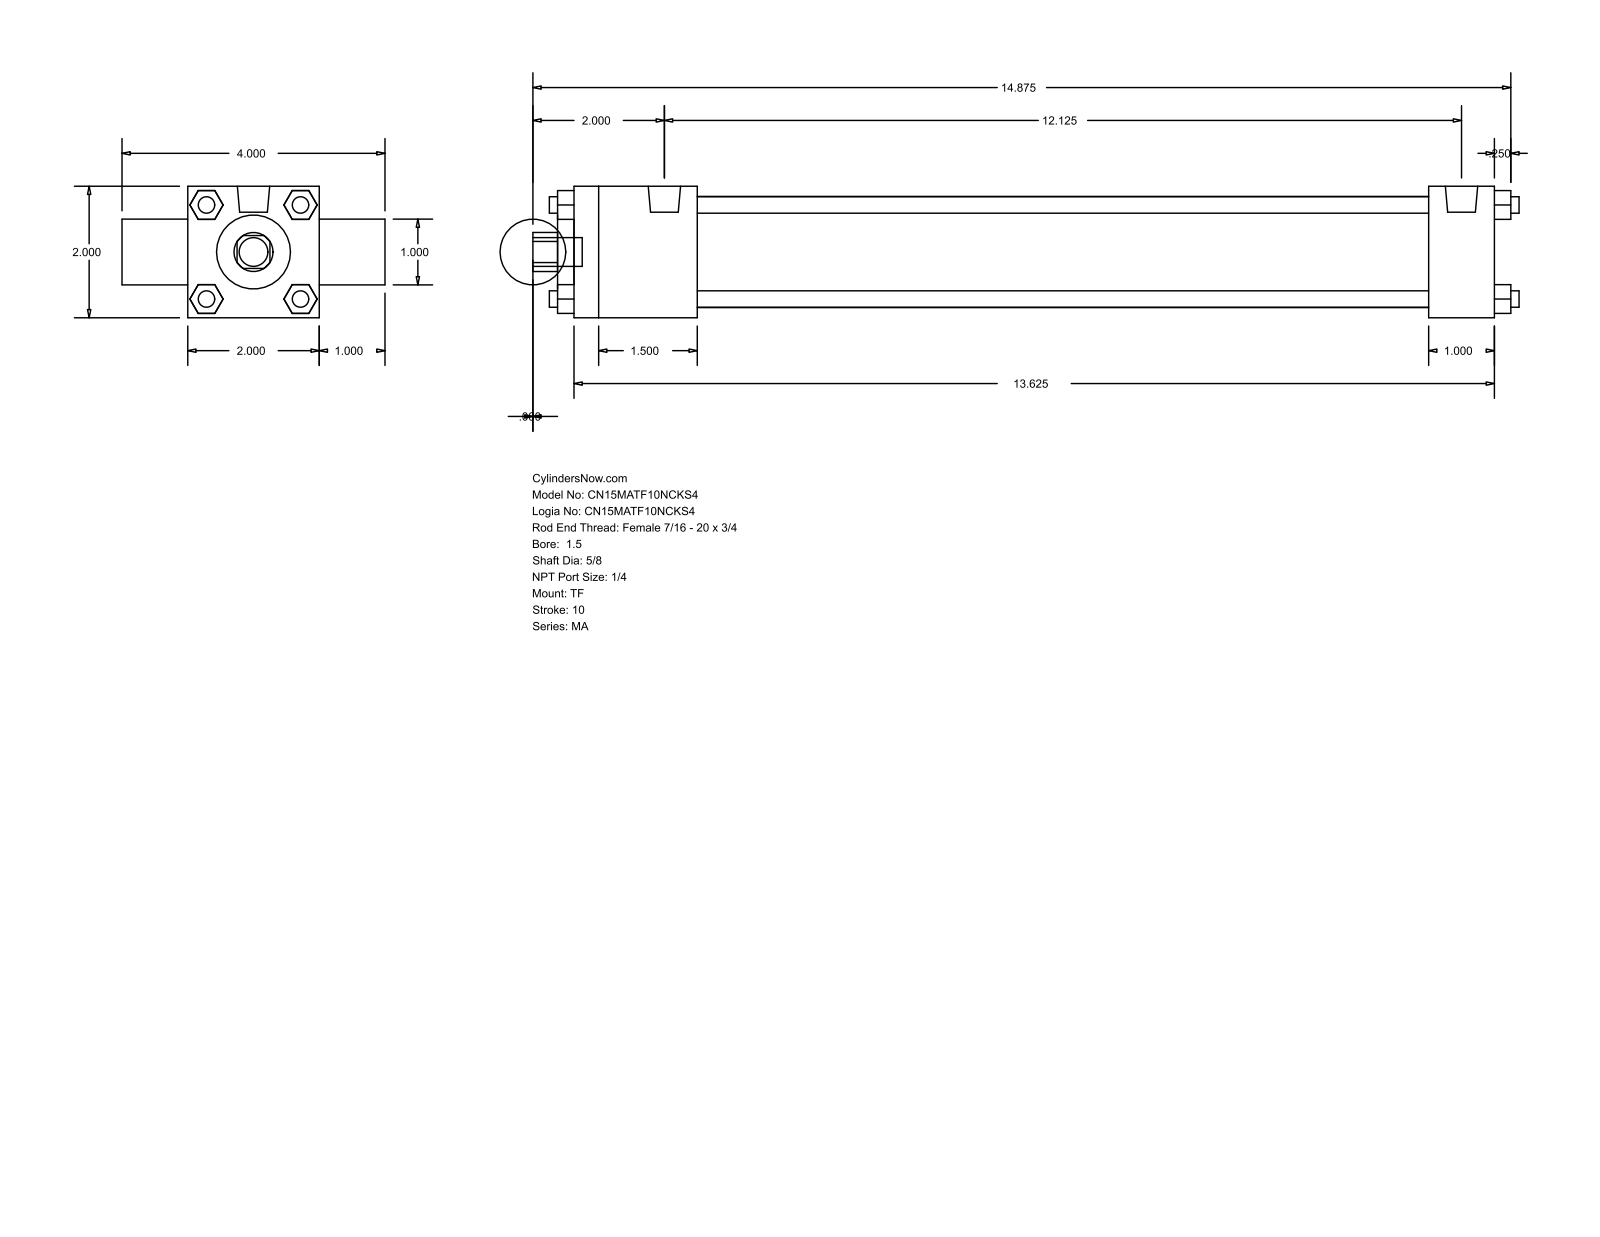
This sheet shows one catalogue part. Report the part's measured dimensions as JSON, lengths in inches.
{"part_name": "MA_TF__0150_0.625", "step_written_by": "GSSL Pune (CONFIG_CONTROL_DESIGN)", "units": "inches", "bodies": {"solids": 0, "faces": 120, "planar": 92, "cylindrical": 28, "other": 0}, "overall_size": [15, 4, 2], "round_holes": [[0.625, 1], [1, 1], [1.125, 1], [1.69, 1]], "round_bosses_or_shafts": [[0.25, 4], [0.313, 3], [0.492, 2], [0.437, 1]], "partial_cylinders_radius": [[0.297, 1]], "face_to_face_distances": [2, 14, 1, 3, 1.875, 13, 11.125, 12.125, 1, 14.25]}
